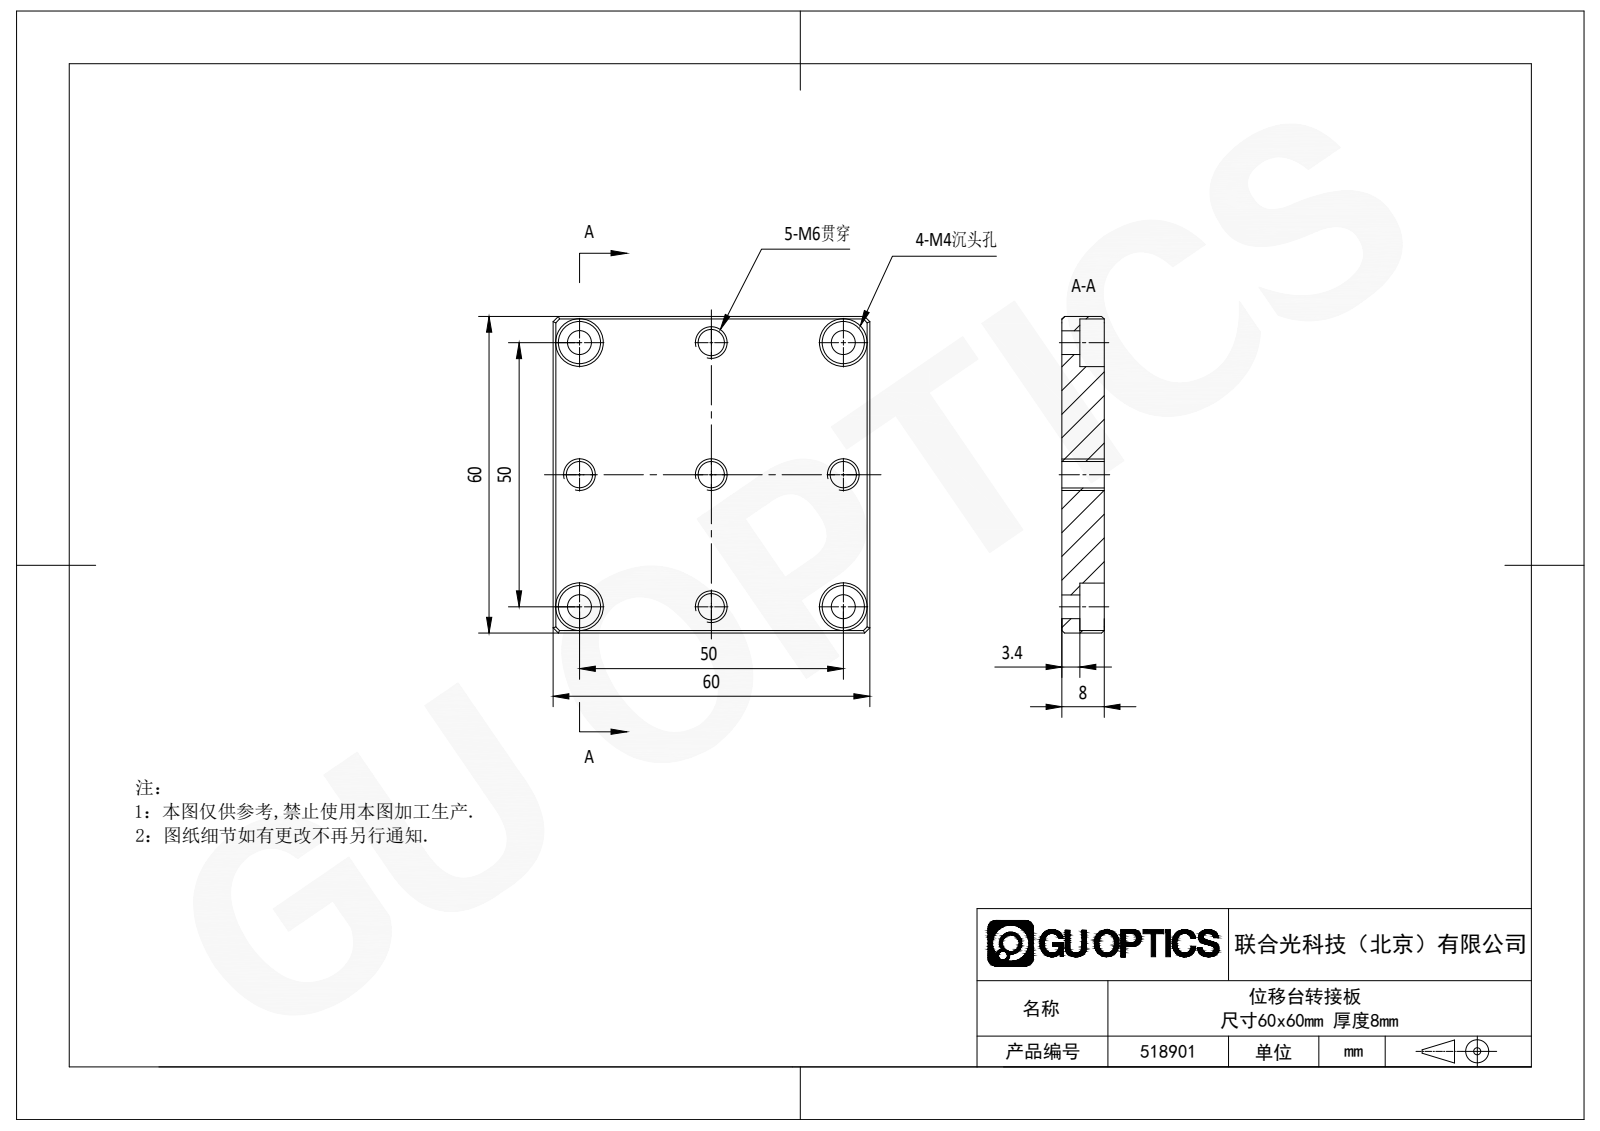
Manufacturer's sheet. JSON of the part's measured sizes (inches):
{"step_written_by": "SolidWorks 2020 (CONFIG_CONTROL_DESIGN)", "units": "inches", "bodies": {"solids": 1, "faces": 56, "planar": 34, "cylindrical": 13, "other": 9}, "overall_size": [2.362, 2.362, 0.315], "volume_in3": 1.633, "surface_area_in2": 15.28, "round_holes": [[0.197, 5], [0.177, 4], [0.315, 4]], "face_to_face_distances": [0.315, 2.362, 1.865, 0.134, 0.181, 3.284, 2.518], "hole_center_spacings": [0.984, 1.392, 2.201, 1.969, 2.784]}
